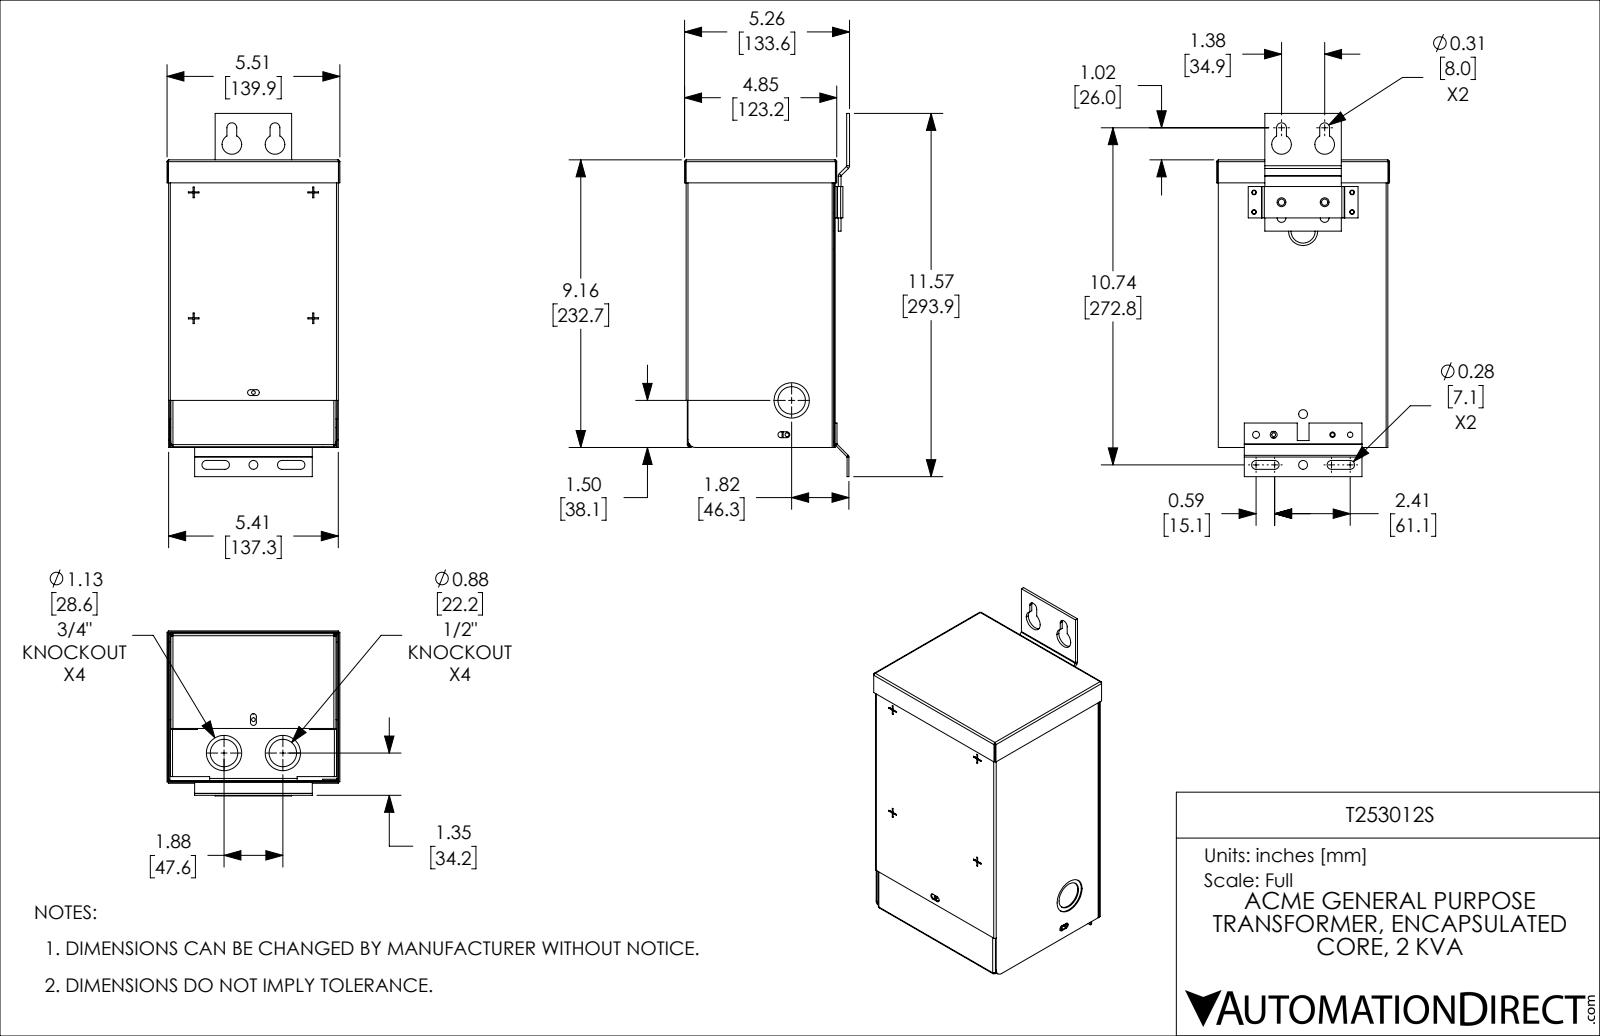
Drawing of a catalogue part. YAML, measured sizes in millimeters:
part_name: "T253012S"
step_written_by: "SolidWorks 2021 (CONFIG_CONTROL_DESIGN)"
units: millimeters
bodies: {solids: 7, faces: 521, planar: 329, cylindrical: 152, other: 40}
overall_size: [293.87, 139.9, 133.57]
volume: 177414
surface_area: 368059
round_holes:
  - {diameter: 7.14, count: 6}
  - {diameter: 3.05, count: 5}
  - {diameter: 22.22, count: 3}
  - {diameter: 28.57, count: 3}
  - {diameter: 4.37, count: 2}
  - {diameter: 4.76, count: 2}
  - {diameter: 5.11, count: 2}
  - {diameter: 5.56, count: 2}
  - {diameter: 15.88, count: 2}
round_bosses_or_shafts:
  - {diameter: 29.79, count: 1}
  - {diameter: 23.44, count: 1}
partial_cylinders:
  - {radius: 0.51, count: 10}
  - {radius: 2.38, count: 10}
  - {radius: 0.79, count: 8}
  - {radius: 1.42, count: 8}
  - {radius: 1.7, count: 8}
  - {radius: 0.38, count: 4}
  - {radius: 1.9, count: 4}
  - {radius: 3.57, count: 4}
face_to_face_distances: [0.91, 119.74, 136.41, 118.83, 135.5, 137.32, 120.65, 231.14, 1.29, 2.2]
hole_center_spacings: [34.92, 12.7, 14.29, 29.09, 34.08, 35.98, 37.16, 41.6]
